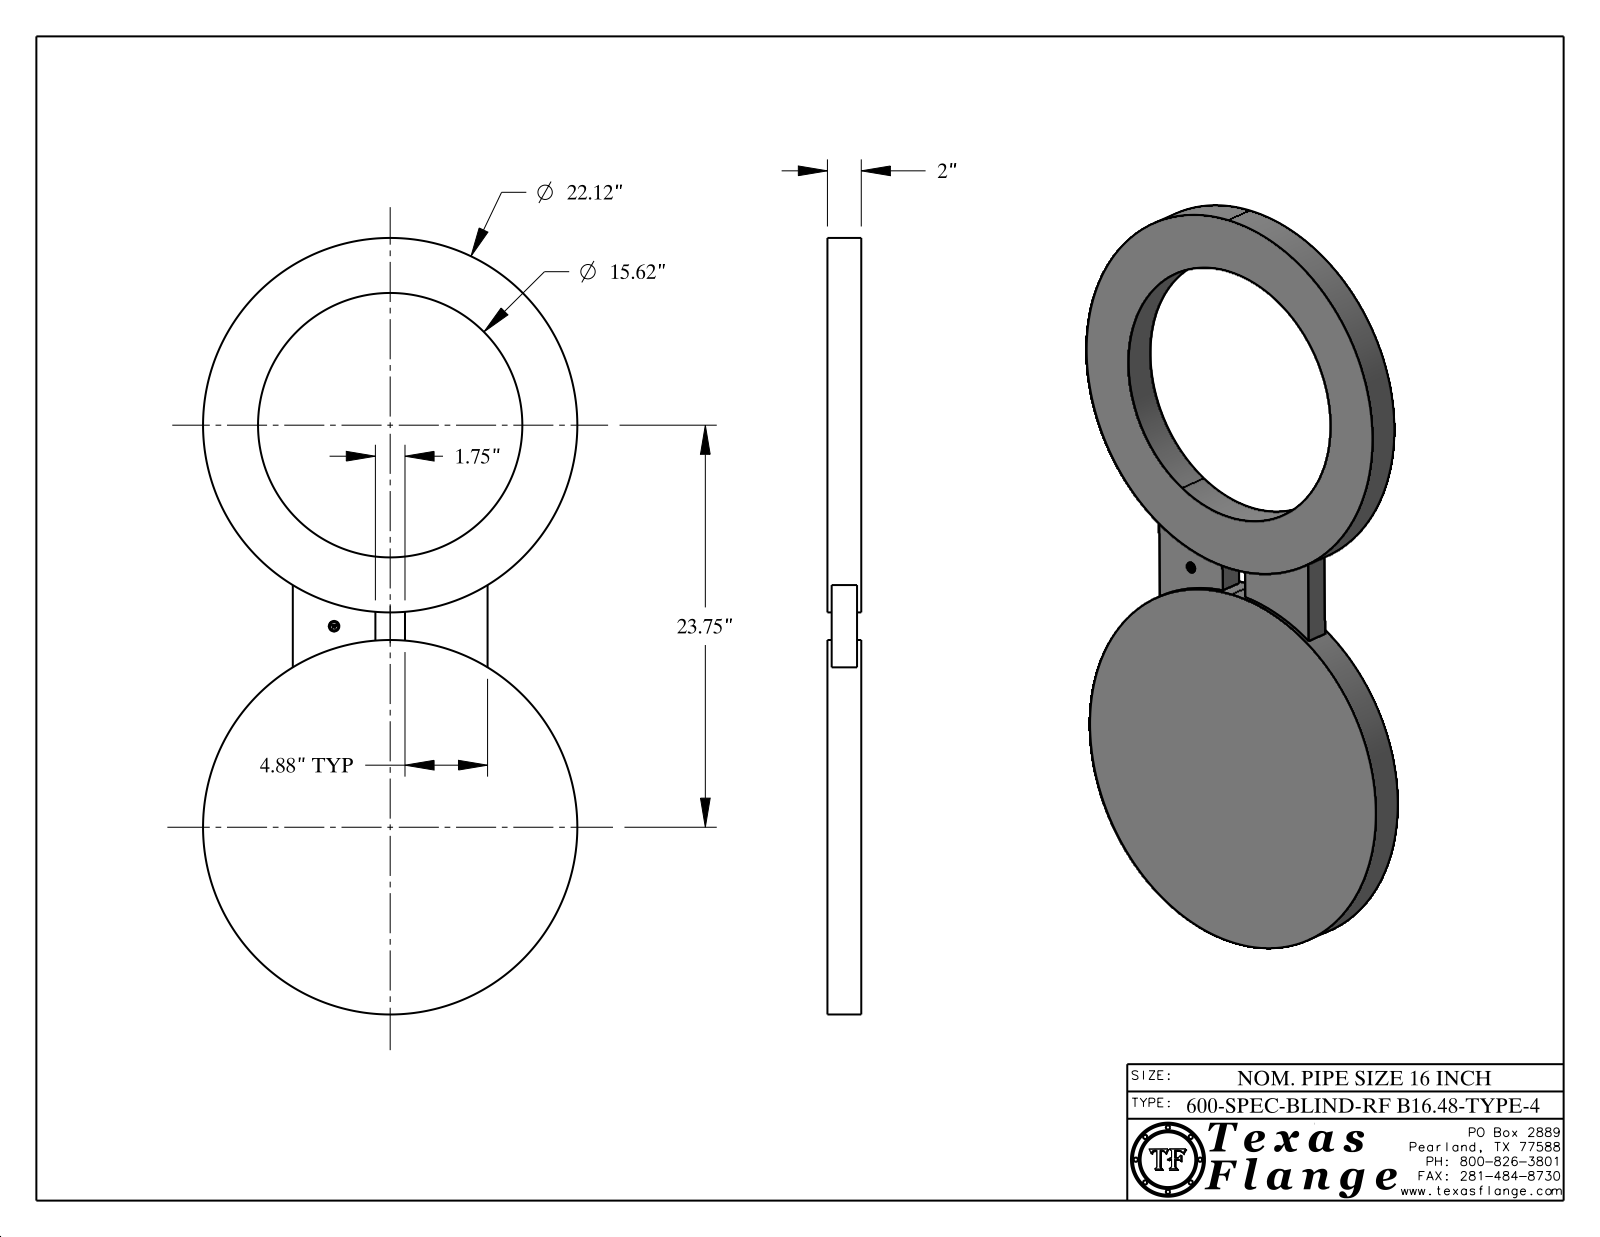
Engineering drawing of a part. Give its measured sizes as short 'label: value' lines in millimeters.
name: 16-600-SPEC-BLIND-RF-B16.48-TYPE-4
written by: CATIA V5 STEP AP214 (AUTOMOTIVE_DESIGN)
unit: mm
bodies: 1 solid, 403 faces (377 planar, 26 cylindrical, 0 other)
size: 1165.1 × 561.8 × 50.8
volume: 19 600 000 mm³; area: 1 016 000 mm²
holes: 1× ⌀15.9, 1× ⌀396.7
bosses: 8× ⌀1, 2× ⌀561.8, 1× ⌀12.5
face distances: 50.8, 6.4, 44.5, 38.1, 292.4, 124, 168.4, 44.5, 44.1, 37.7
hole spacings: 313.2
